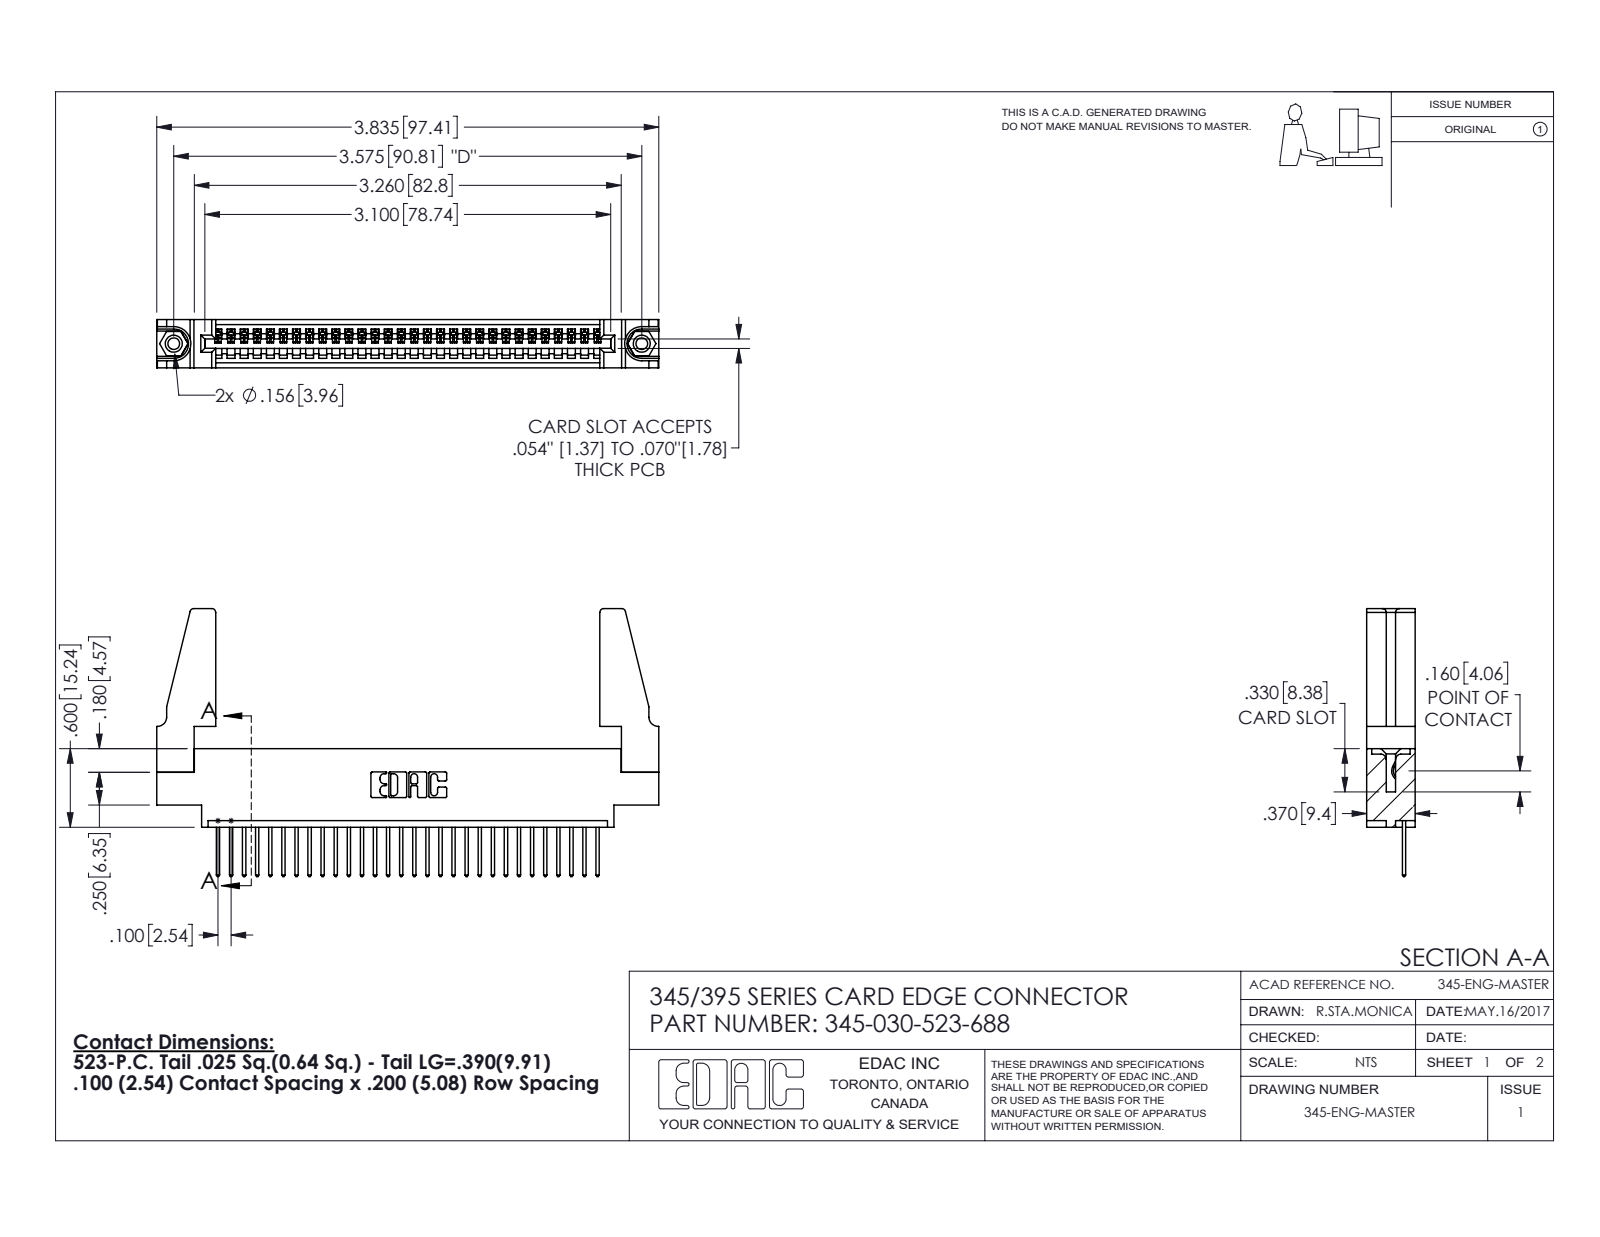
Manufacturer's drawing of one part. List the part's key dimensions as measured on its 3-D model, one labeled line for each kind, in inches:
Part name (STEP PRODUCT): 345-030-523-688; 345-220-078_345-220-088; 345 Part_0.170 Offset - 0.156 Dia-TH; 345-292-001_345-293-123 (+1 more)
STEP written by: SolidWorks 2016 (CONFIG_CONTROL_DESIGN)
Units: inches
Bodies: 35 solids, 1994 faces (1356 planar, 622 cylindrical, 16 other)
Overall size (bounding box): 3.836 × 2.047 × 0.37
Volume: 0.75 in³ · Surface area: 23.45 in²
Round holes (diameter × count): ⌀0.089 ×2, ⌀0.125 ×2, ⌀0.156 ×2, ⌀0.064 ×1
Round bosses / shafts (diameter × count): ⌀0.155 ×2
Partial cylindrical surfaces — rounded edges, fillets, slot ends (radius × count): R0.006 ×60, R0.01 ×60, R0.01 ×22, R0.03 ×8, R0.007 ×6, R0.031 ×6, R0.026 ×3, R0.031 ×2
Main face-to-face distances: 0.37, 0.072, 0.298, 0.098, 0.272, 0.025, 0.2, 0.225, 0.175, 0.149
Hole centre spacings: 0.27, 3.34, 3.575
